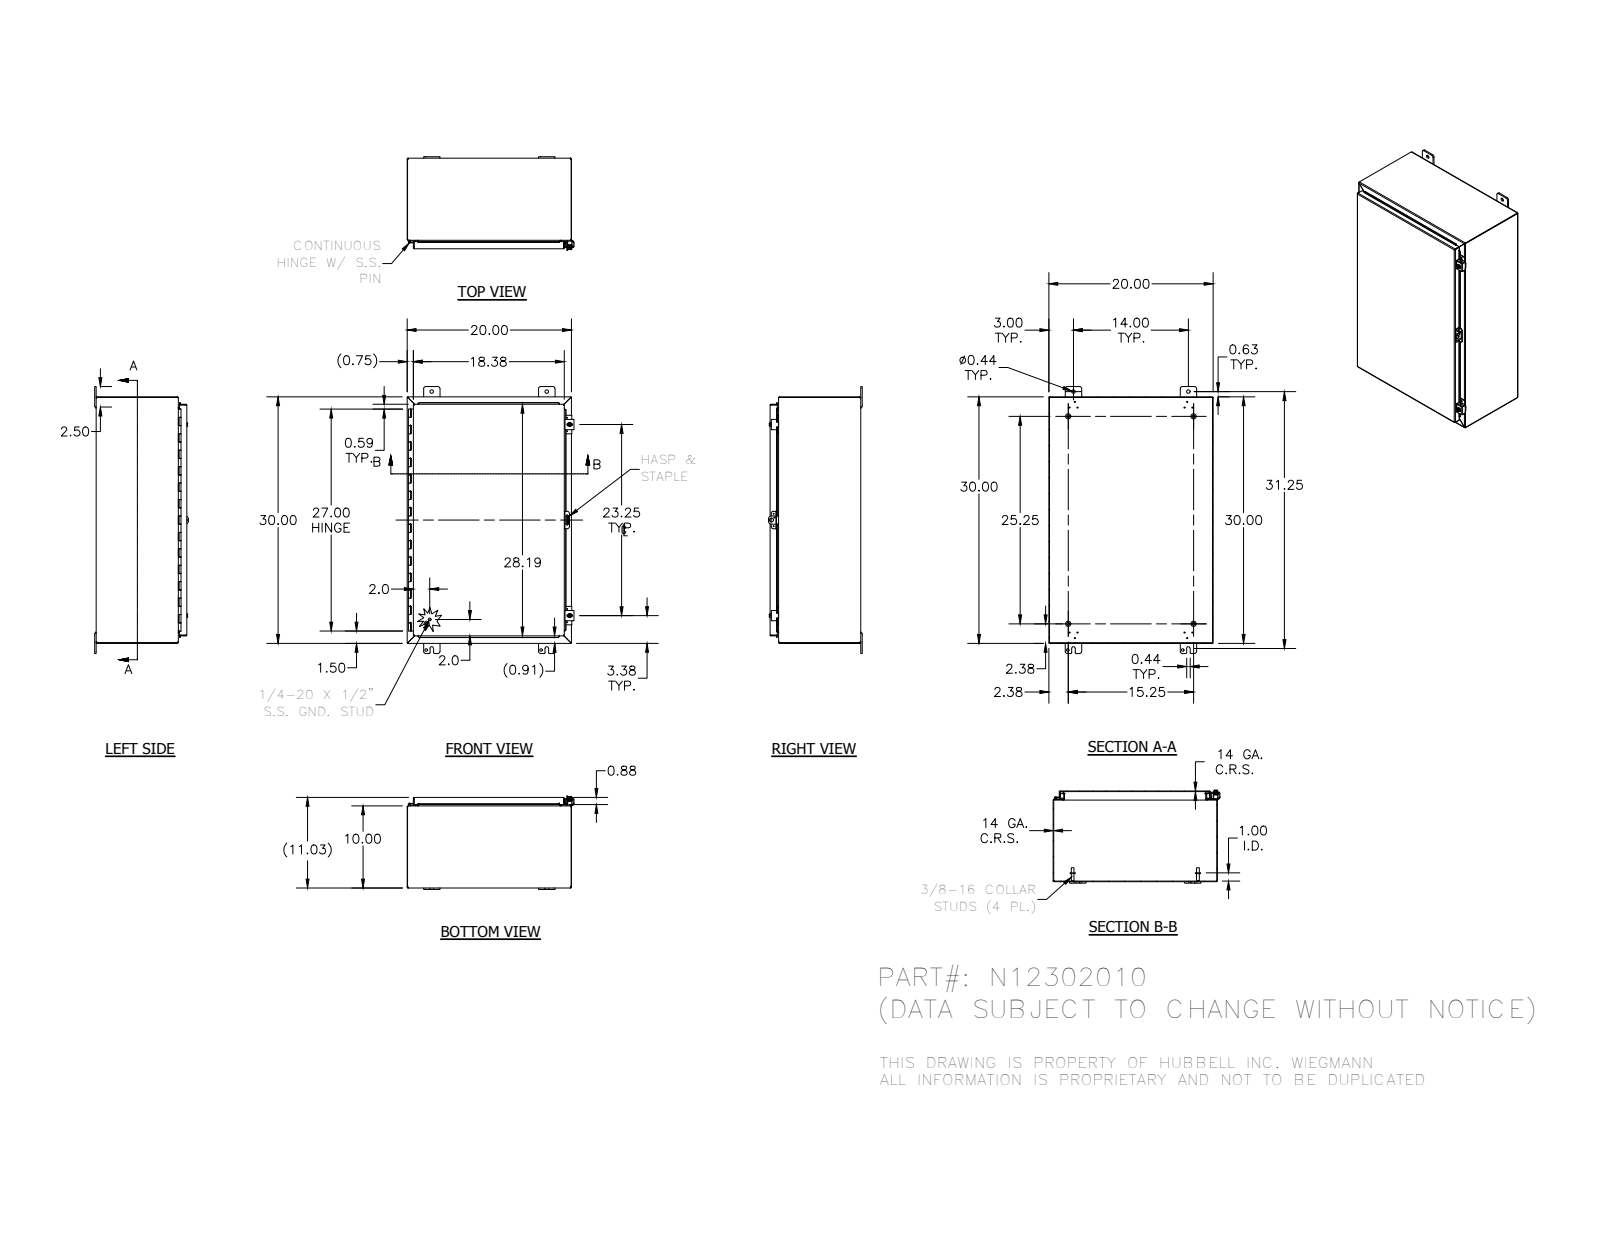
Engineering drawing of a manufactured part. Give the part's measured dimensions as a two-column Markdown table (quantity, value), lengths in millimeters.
| quantity | value |
| --- | --- |
| part name | N12302010; 34840; 38420; N12302010BKP (+8 more) |
| STEP written by | Autodesk Inventor 2012 (AUTOMOTIVE_DESIGN) |
| units | millimeters |
| bodies | 27 solids, 1033 faces (566 planar, 350 cylindrical, 117 other) |
| overall size | 825.5 × 515.9 × 289.8 |
| volume | 3 214 000 mm³ |
| surface area | 3 320 000 mm² |
| round holes (diameter × count) | 3 × 12, 2.8 × 7, 8 × 4, 11.1 × 4, 5.4 × 2, 7.1 × 2, 7.6 × 2, 3.2 × 1, 4 × 1, 12.7 × 1 |
| round bosses / shafts (diameter × count) | 15.9 × 4, 8.4 × 4, 6.4 × 4, 13.2 × 2, 12.7 × 2, 8.9 × 2, 2.9 × 2, 8.6 × 1 |
| partial cylindrical surfaces (radius × count) | 0.8 × 27, 1.6 × 25, 3.2 × 25, 6.4 × 25, 0.8 × 23, 2.7 × 23, 1.8 × 8, 2.5 × 4 |
| main face-to-face distances | 1.9, 278.4, 506.1, 276.5, 280.2, 760.1, 504.2, 508, 252.1, 26.2 |
| hole center spacings | 355.6, 19.3, 23.9, 24.6, 50.7, 339.7, 364.3, 695.5 |
